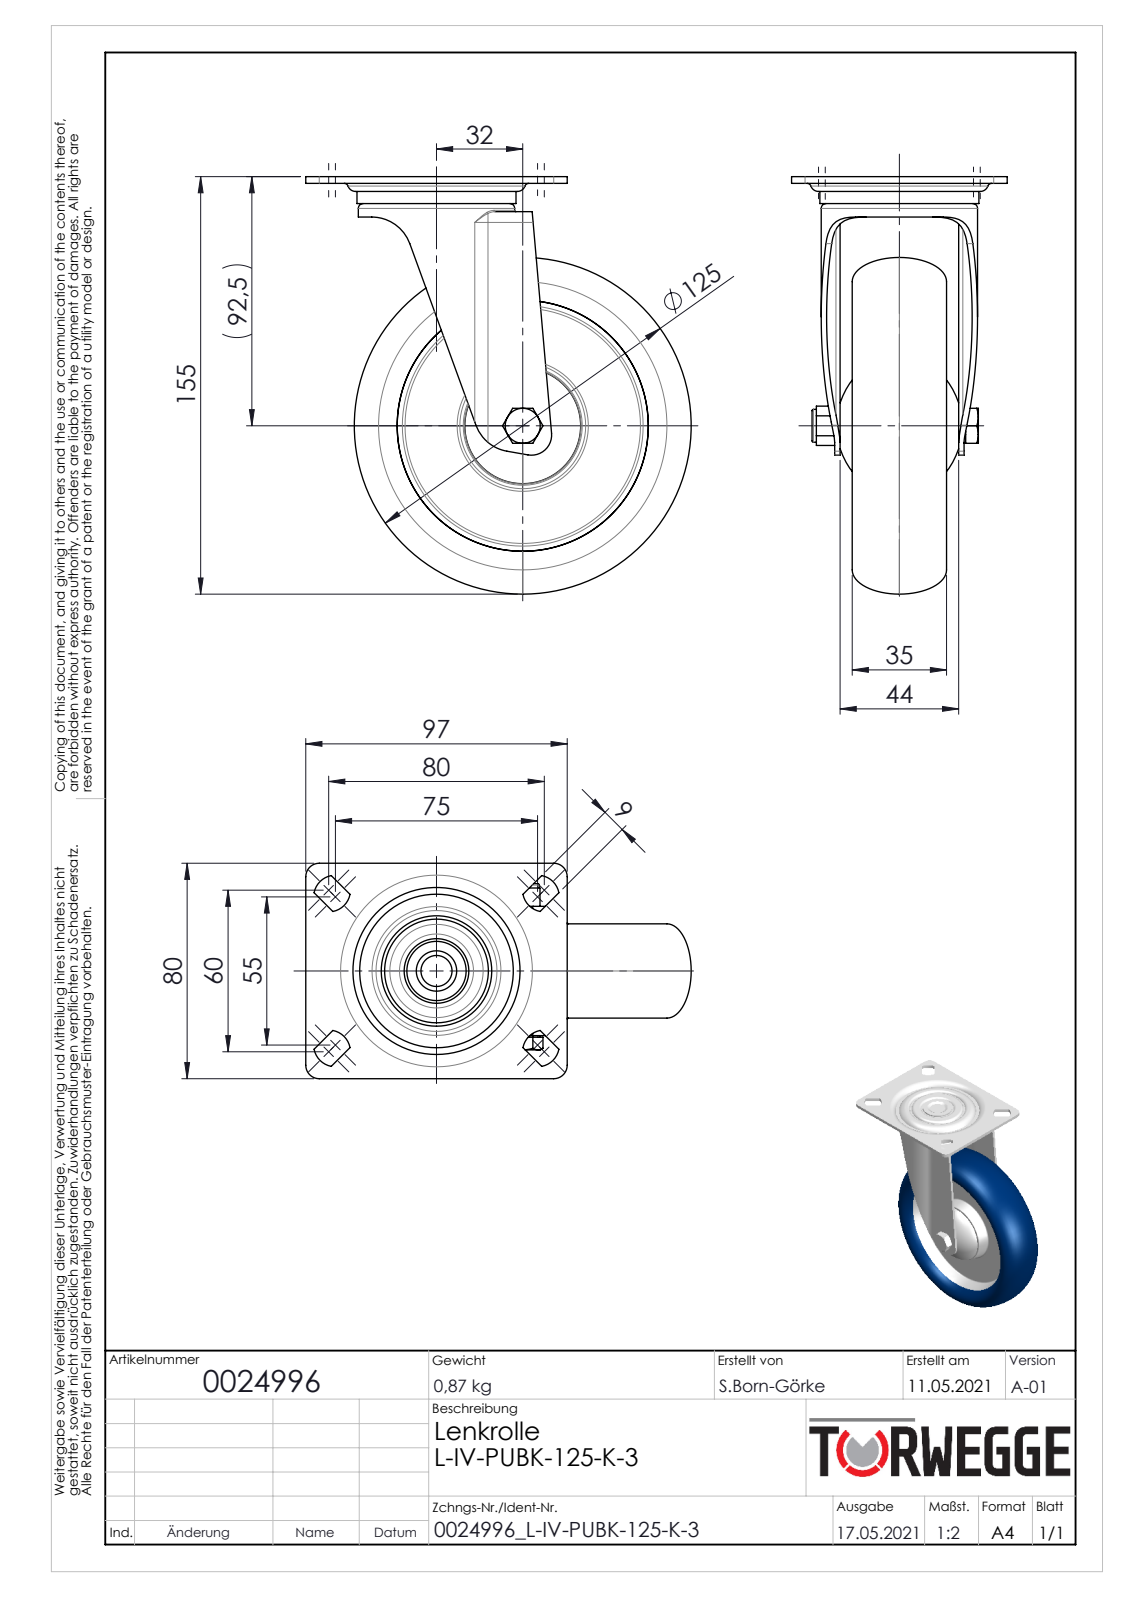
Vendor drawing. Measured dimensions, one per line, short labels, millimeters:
name: 0024996
written by: SolidWorks 2020 (AUTOMOTIVE_DESIGN)
unit: mm
bodies: 7 solids, 248 faces (76 planar, 64 cylindrical, 108 other)
size: 155 × 143 × 80
volume: 292 580 mm³; area: 122 572 mm²
holes: 1× ⌀6.65, 1× ⌀8, 1× ⌀8.2, 1× ⌀33, 1× ⌀35, 1× ⌀54
bosses: 1× ⌀59, 1× ⌀58, 1× ⌀29, 1× ⌀22, 1× ⌀15, 1× ⌀13, 1× ⌀12.2
rounds: 8× R8.07, 4× R5, 2× R2, 2× R4, 2× R10, 2× R12, 2× R15, 1× R7.5
face distances: 5, 2, 2.5, 21.5, 19.5, 24.5, 26.5, 46, 12, 13.25
